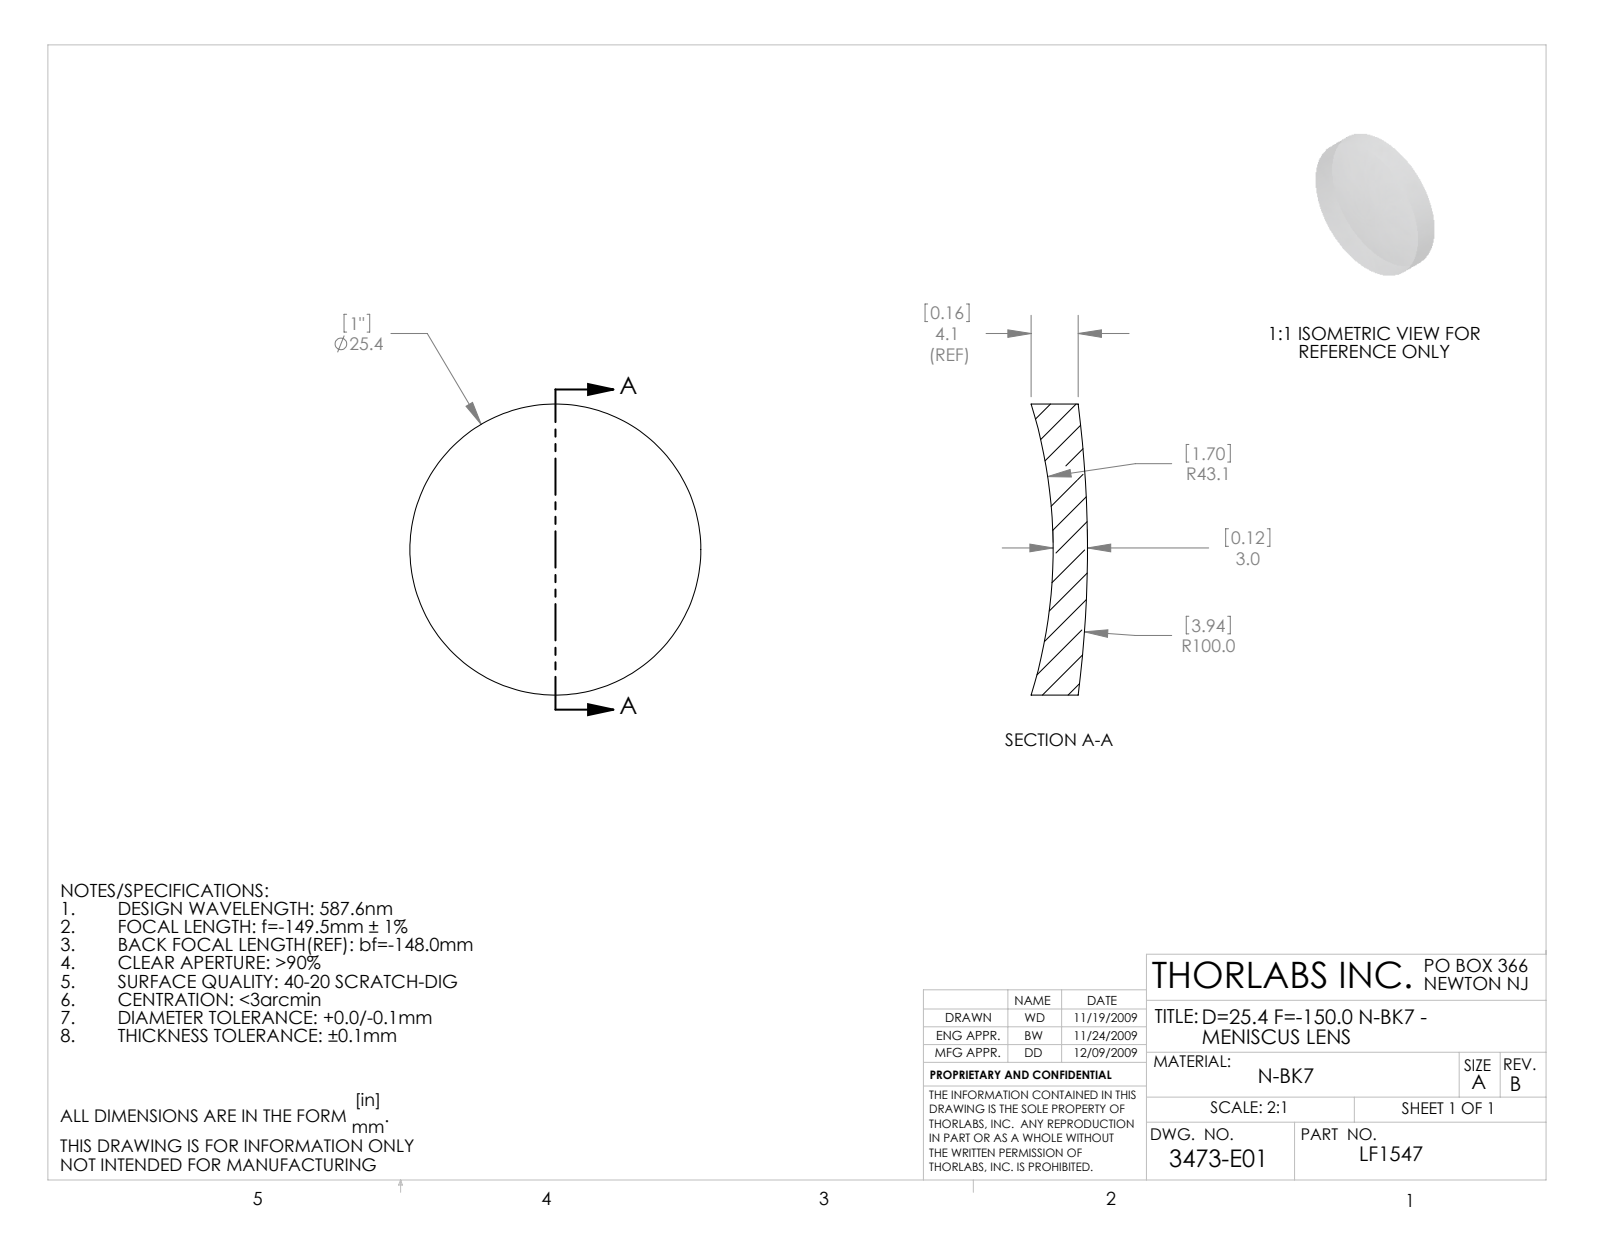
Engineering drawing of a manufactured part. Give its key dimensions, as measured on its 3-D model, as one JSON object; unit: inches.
{"part_name": "3473-E0W", "step_written_by": "SolidWorks 2009 (AUTOMOTIVE_DESIGN)", "units": "inches", "bodies": {"solids": 1, "faces": 6, "planar": 0, "cylindrical": 2, "other": 4}, "overall_size": [1, 1, 0.193], "volume_in3": 0.11, "surface_area_in2": 2.099, "round_bosses_or_shafts": [[1, 1]]}
